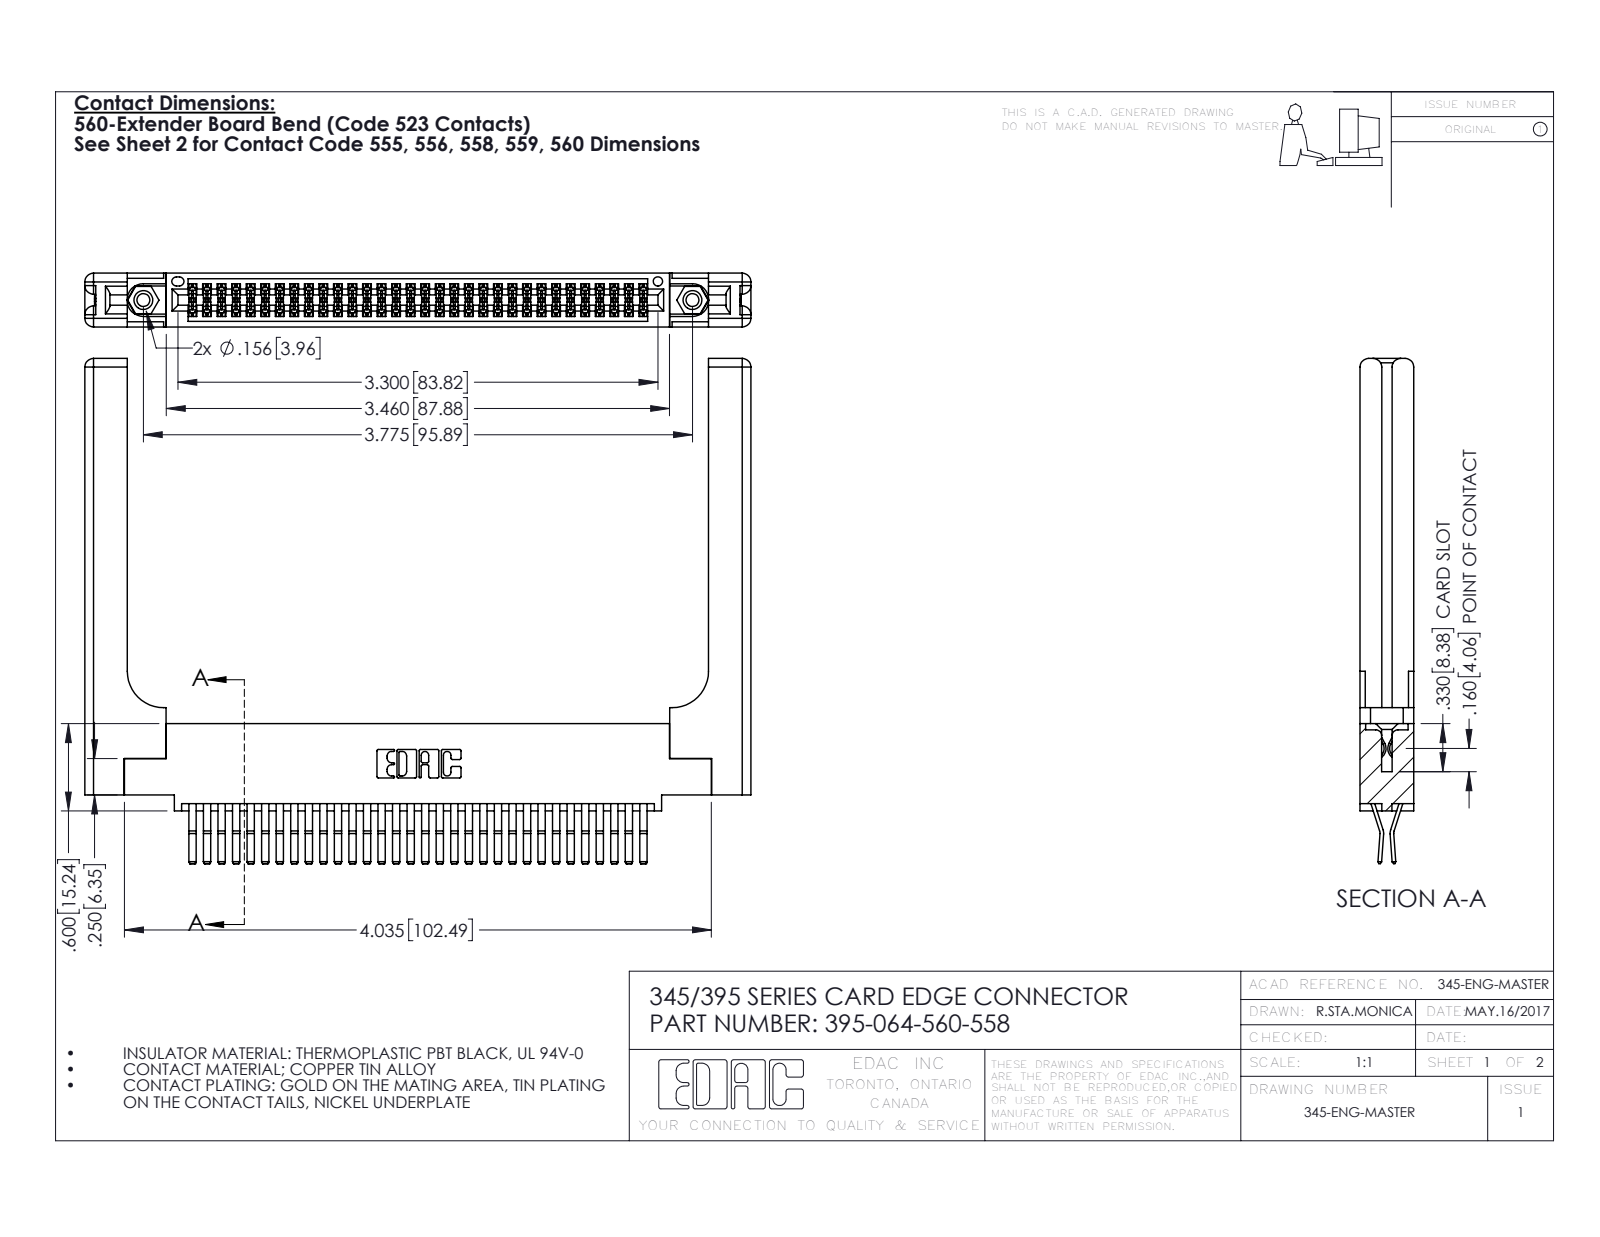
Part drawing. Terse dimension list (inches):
name: 395-064-560-558; 345-220-058_345-220-058; 345 Part_0.110 Offset - 0.156 Dia-TH; 345-292-001_560 Tail (+1 more)
written by: SolidWorks 2016 (CONFIG_CONTROL_DESIGN)
unit: in
bodies: 69 solids, 3714 faces (2344 planar, 1310 cylindrical, 60 other)
size: 4.579 × 3.472 × 0.37
volume: 1.222 in³; area: 35.82 in²
holes: 2× ⌀0.089, 2× ⌀0.125, 2× ⌀0.156, 1× ⌀0.064
bosses: 2× ⌀0.155
rounds: 97× R0.006, 22× R0.01, 16× R0.06, 6× R0.007, 6× R0.031, 3× R0.026, 2× R0.01, 2× R0.014
face distances: 0.37, 0.072, 0.298, 0.025, 0.225, 0.098, 0.272, 0.2, 0.148, 0.15
hole spacings: 0.27, 3.54, 3.775
